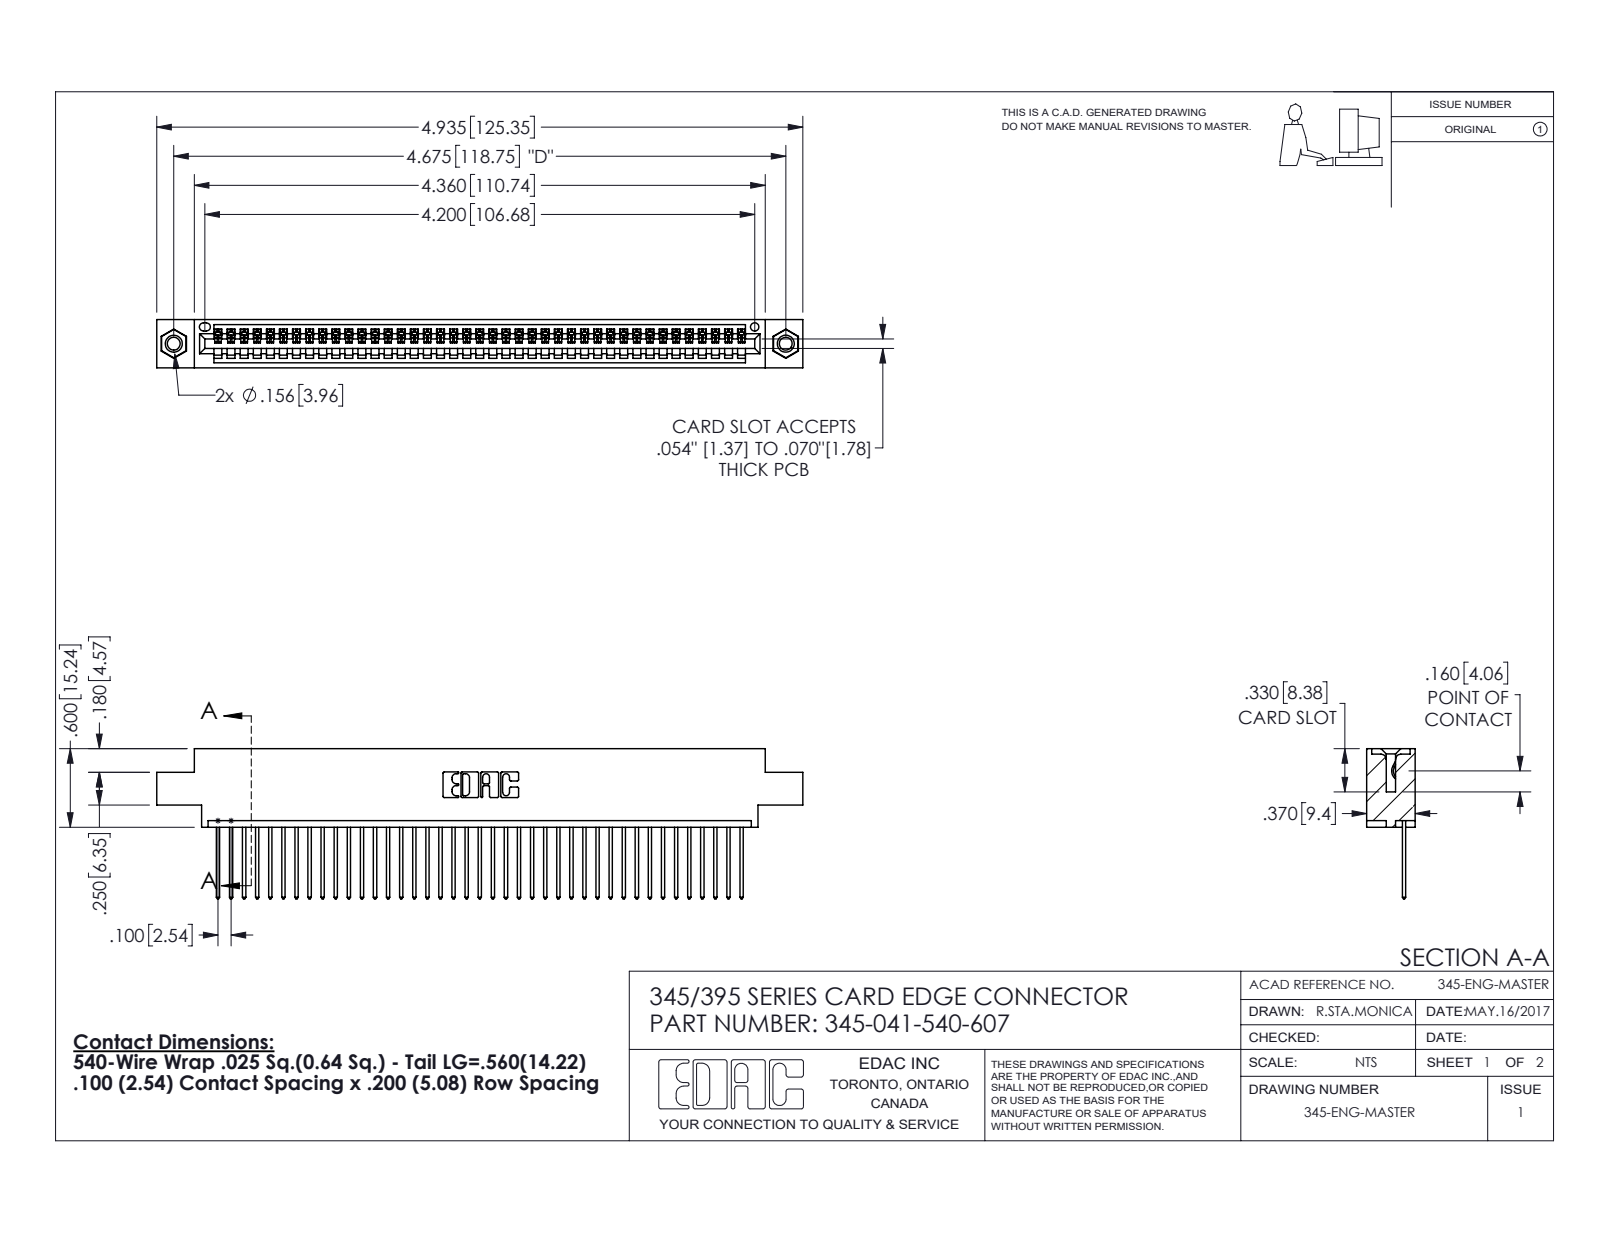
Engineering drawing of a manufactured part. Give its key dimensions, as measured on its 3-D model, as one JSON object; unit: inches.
{"part_name": "345-041-540-607; 345-250-001_345-250-005-103; 345 Part_0.170 Offset - 0.156 Dia-TI; 345-292-001_345-293-140", "step_written_by": "SolidWorks 2016 (CONFIG_CONTROL_DESIGN)", "units": "inches", "bodies": {"solids": 44, "faces": 2568, "planar": 1756, "cylindrical": 796, "other": 16}, "overall_size": [4.935, 1.147, 0.37], "volume_in3": 0.722, "surface_area_in2": 25.2, "round_holes": [[0.098, 2], [0.125, 2], [0.156, 2], [0.064, 1]], "round_bosses_or_shafts": [[0.155, 2]], "partial_cylinders_radius": [[0.006, 82], [0.01, 82], [0.01, 22], [0.007, 6], [0.031, 6], [0.026, 3], [0.031, 2], [0.04, 2]], "face_to_face_distances": [0.072, 0.298, 0.37, 0.098, 0.272, 0.025, 0.2, 0.225, 0.175, 0.149], "hole_center_spacings": [0.27, 4.439, 4.675]}
